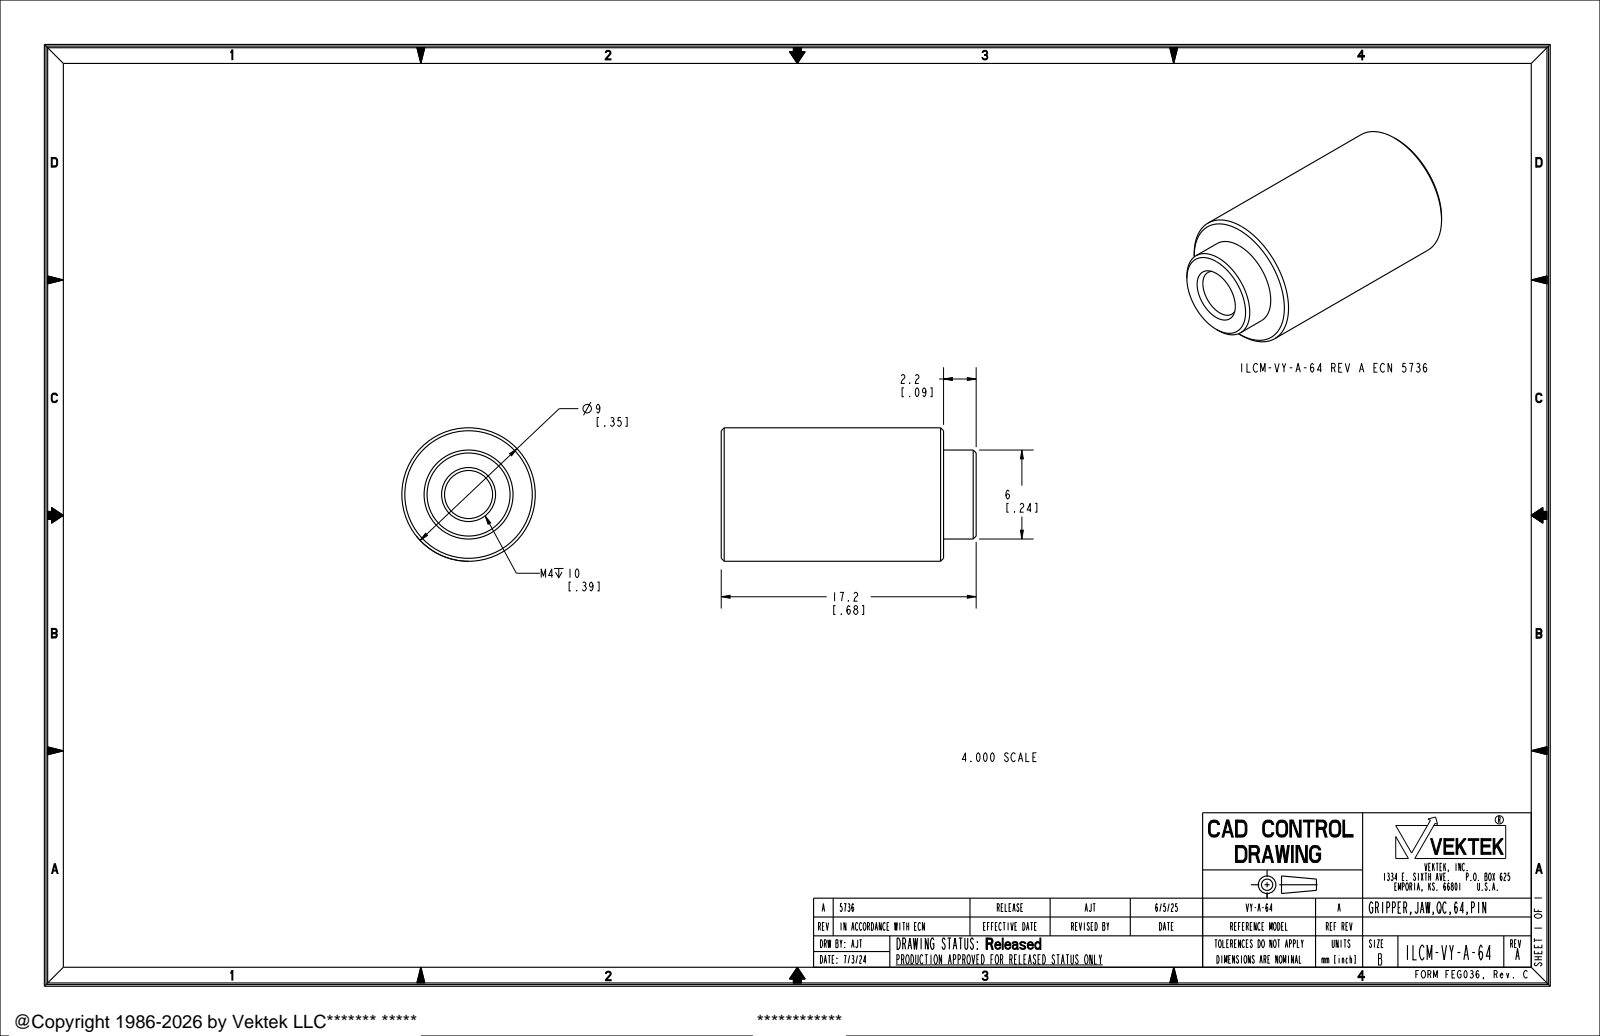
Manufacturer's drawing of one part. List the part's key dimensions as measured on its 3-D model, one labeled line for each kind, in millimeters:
Part name (STEP PRODUCT): ILCM-VY-A-64
STEP written by: CREO PARAMETRIC BY PTC INC, 2021164 (AUTOMOTIVE_DESIGN)
Units: millimetres
Bodies: 1 solid, 28 faces (12 planar, 8 cylindrical, 8 other)
Overall size (bounding box): 17.2 × 9 × 9
Volume: 894 mm³ · Surface area: 864 mm²
Round holes (diameter × count): ⌀3.24 ×1
Round bosses / shafts (diameter × count): ⌀9 ×1, ⌀6 ×1, ⌀4 ×1
Main face-to-face distances: 15, 3, 17.2, 2.2, 5.4, 9.6, 11.8, 2.4, 12, 14.2
